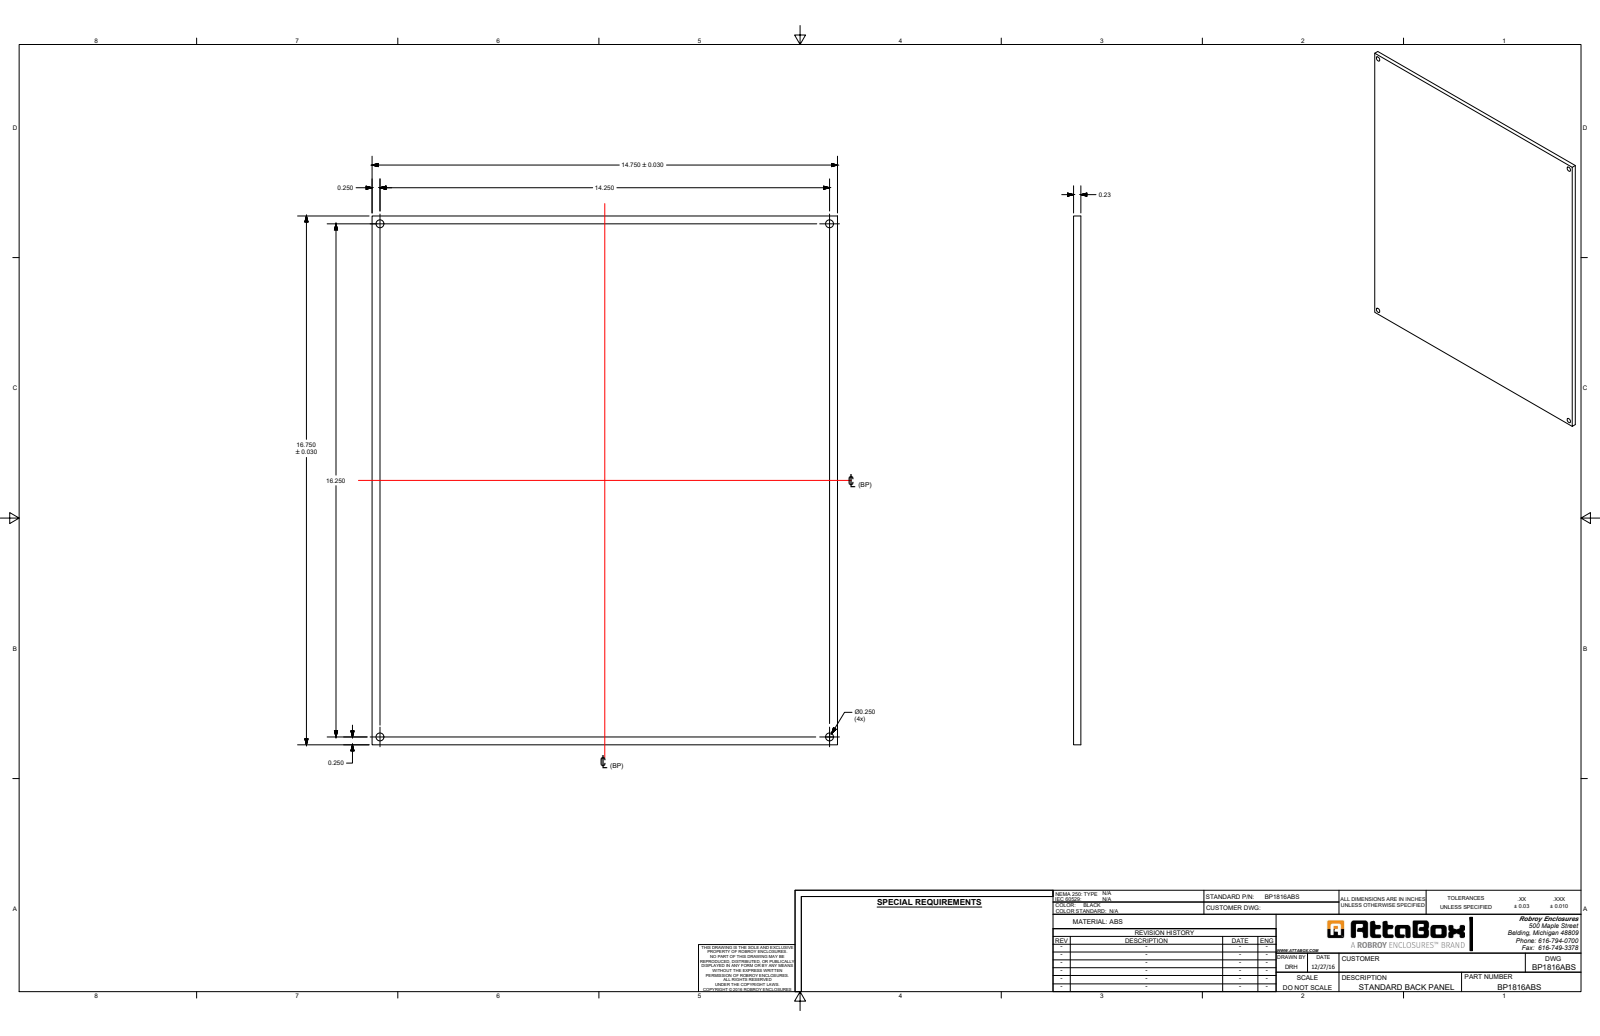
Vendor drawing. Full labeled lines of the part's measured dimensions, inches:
Part name (STEP PRODUCT): BP1816ABS_Default
STEP written by: SolidWorks 2023 (CONFIG_CONTROL_DESIGN)
Units: inches
Bodies: 1 solid, 10 faces (6 planar, 4 cylindrical, 0 other)
Overall size (bounding box): 16.75 × 14.75 × 0.23
Volume: 56.78 in³ · Surface area: 508.9 in²
Round holes (diameter × count): ⌀0.25 ×4
Main face-to-face distances: 0.23, 14.75, 16.75
Hole centre spacings: 14.25, 16.25, 21.613
